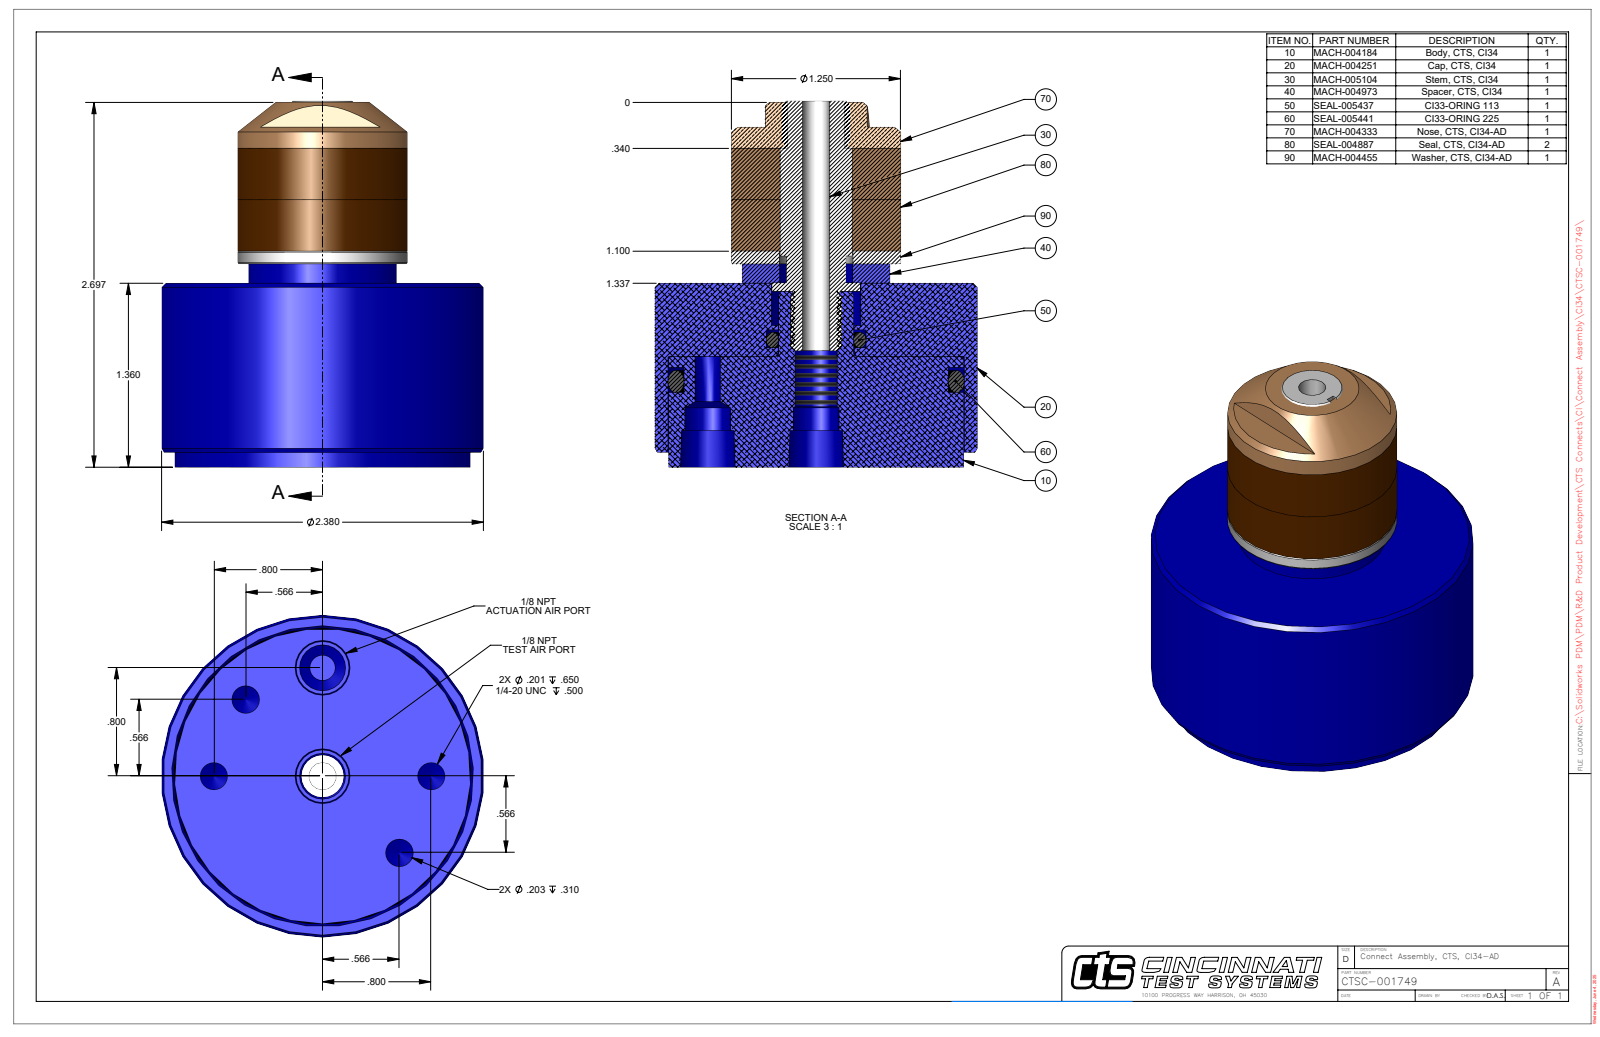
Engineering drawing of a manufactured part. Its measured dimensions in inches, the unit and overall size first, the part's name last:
Units: inches
Overall size (bounding box): 2.706 × 2.38 × 2.38
Round holes (diameter × count): ⌀0.201 ×2, ⌀0.203 ×2, ⌀0.339 ×2, ⌀0.203 ×1, ⌀2.188 ×1
Round bosses / shafts (diameter × count): ⌀2.38 ×1, ⌀2.178 ×1, ⌀1.25 ×1, ⌀1.09 ×1
Partial cylindrical surfaces — rounded edges, fillets, slot ends (radius × count): R0.211 ×1
Main face-to-face distances: 1.36, 0.11, 1.25, 1.503, 1.393, 0.143, 2.513, 2.403, 1.153, 1.01
Hole centre spacings: 0.8, 0.612, 1.478, 1.131, 1.6
Volume: 7.212 in³ · Surface area: 31.99 in²
Bodies: 1 solid, 76 faces (22 planar, 27 cylindrical, 27 other)
Part name (STEP PRODUCT): CTSC-001749
STEP written by: SolidWorks 2023 (AUTOMOTIVE_DESIGN)
